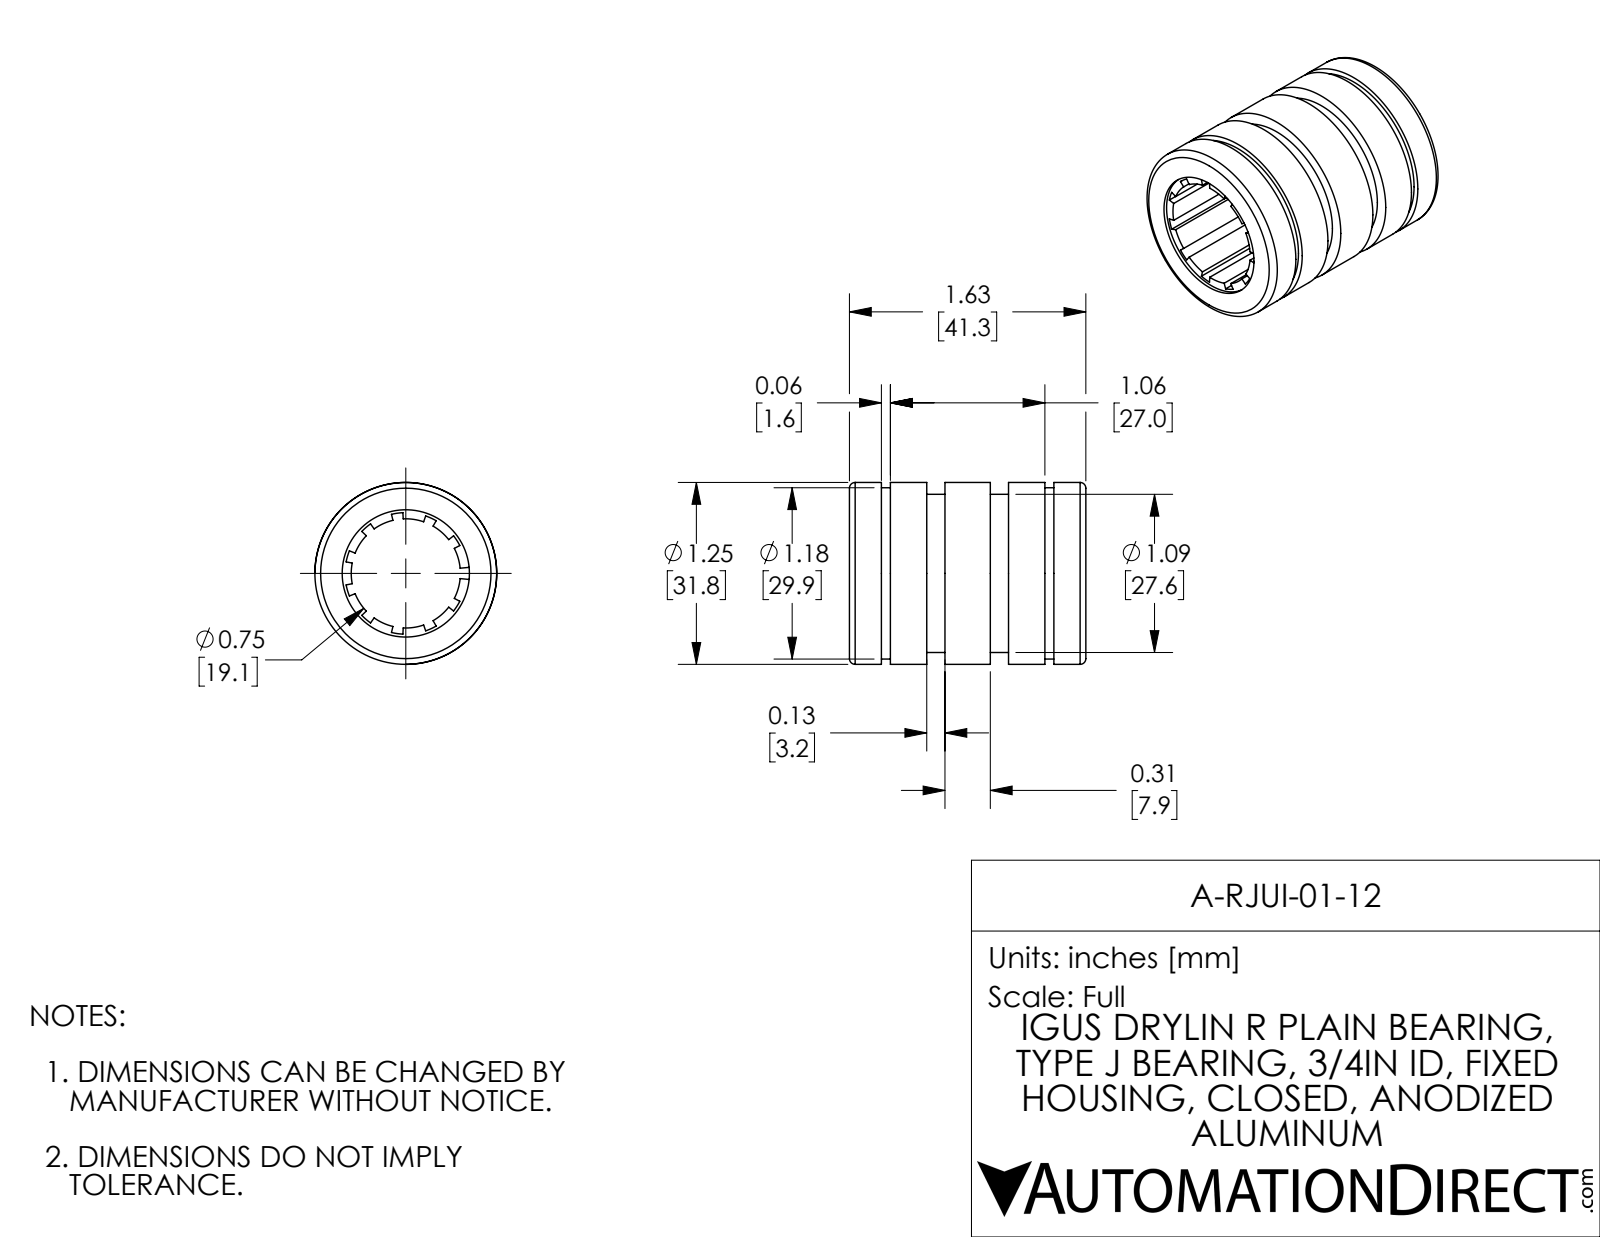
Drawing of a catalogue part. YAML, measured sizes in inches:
part_name: "A-RJUI-01-12"
step_written_by: "SolidWorks 2017 (AUTOMOTIVE_DESIGN)"
units: inches
bodies: {solids: 2, faces: 147, planar: 79, cylindrical: 64, other: 4}
overall_size: [1.625, 1.25, 1.25]
volume: 1.105
surface_area: 23.87
round_holes:
  - {diameter: 0.141, count: 1}
  - {diameter: 0.875, count: 1}
  - {diameter: 0.953, count: 1}
round_bosses_or_shafts:
  - {diameter: 1.25, count: 1}
  - {diameter: 1.177, count: 1}
  - {diameter: 1.087, count: 1}
  - {diameter: 0.875, count: 1}
  - {diameter: 0.134, count: 1}
partial_cylinders:
  - {radius: 0.375, count: 1}
  - {radius: 0.418, count: 1}
  - {radius: 0.469, count: 1}
face_to_face_distances: [0.437, 0.531, 0.657, 0.969, 1.094, 0.125, 0.312, 0.187, 1.625, 0.719]
